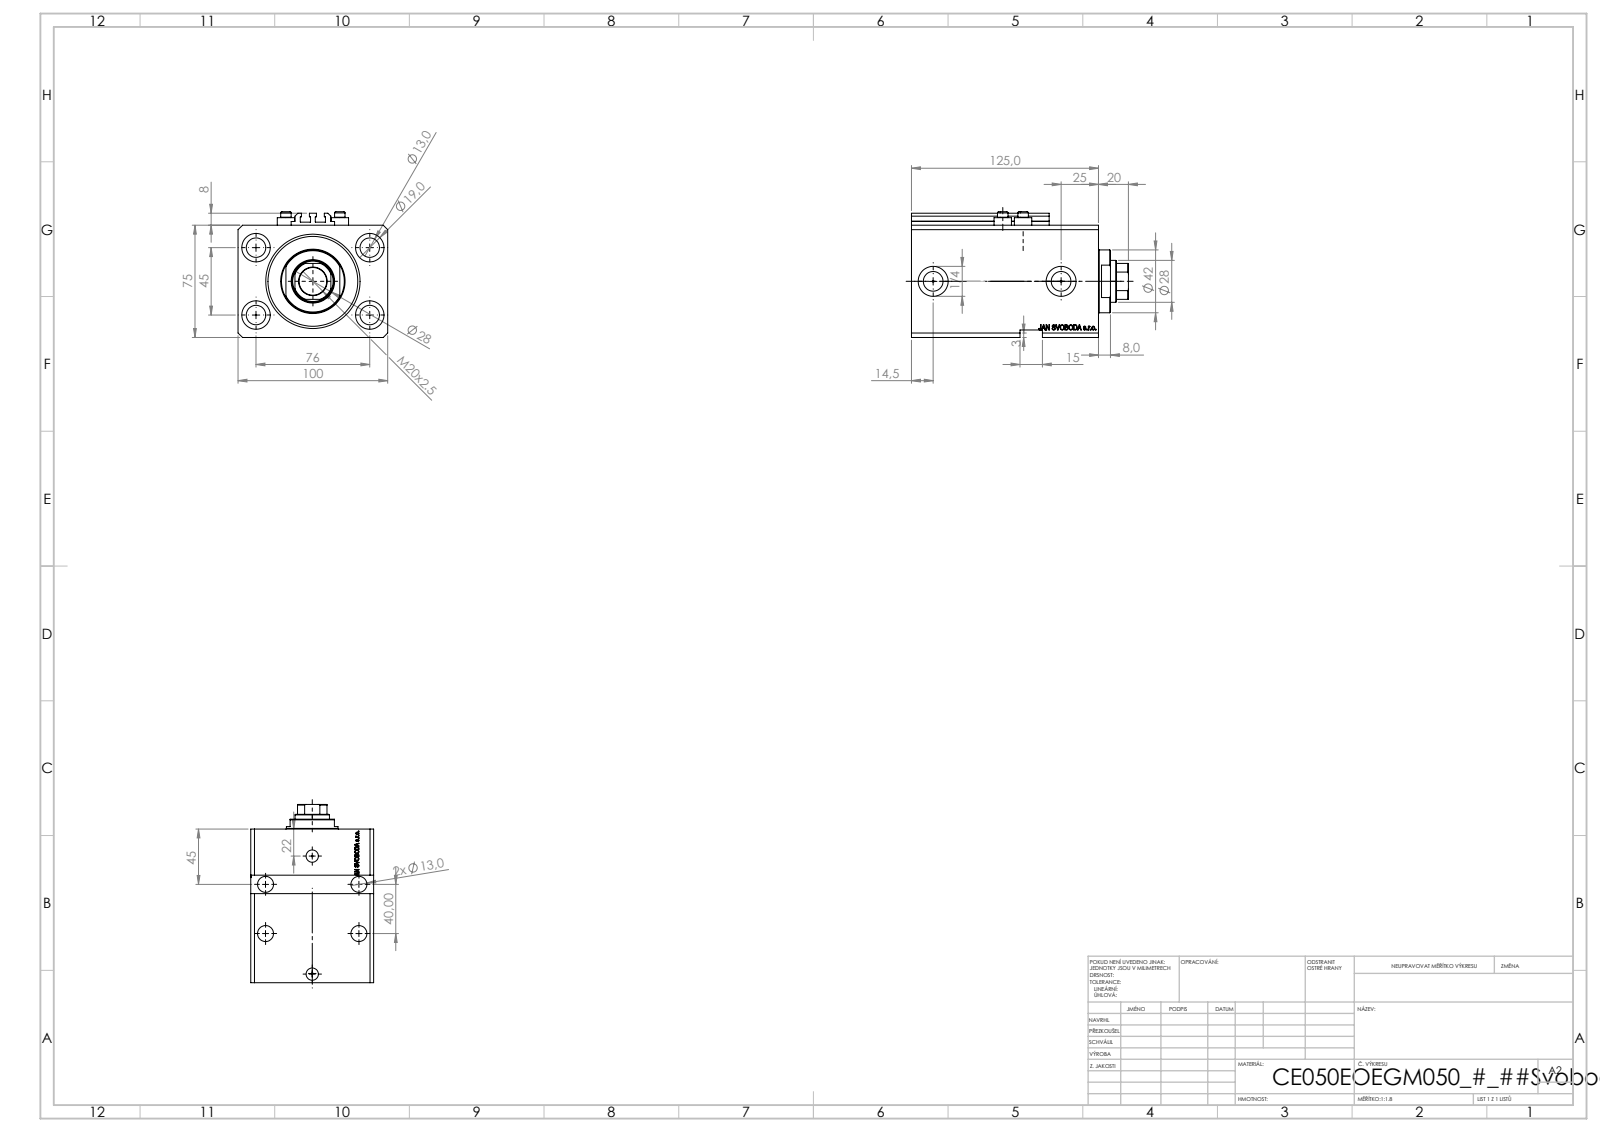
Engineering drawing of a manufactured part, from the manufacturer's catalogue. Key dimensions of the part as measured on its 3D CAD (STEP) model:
Part name (STEP PRODUCT): ALLEN BOLT V250CE; V250CE_E_Body; V250CE_VC_E; V250CE_C_VCP
STEP written by: SolidWorks 2019 (CONFIG_CONTROL_DESIGN)
Units: millimetres
Bodies: 8 solids, 1108 faces (535 planar, 146 cylindrical, 427 other)
Overall size (bounding box): 145 × 100 × 84
Volume: 768 812 mm³ · Surface area: 150 350 mm²
Round holes (diameter × count): ⌀13 ×8, ⌀1.25 ×4, ⌀4 ×4, ⌀19 ×4, ⌀10 ×2, ⌀13.16 ×2, ⌀20 ×2, ⌀18.5 ×1, ⌀28 ×1, ⌀50 ×1, ⌀63 ×1
Round bosses / shafts (diameter × count): ⌀11.6 ×4, ⌀7 ×4, ⌀42 ×1
Partial cylindrical surfaces — rounded edges, fillets, slot ends (radius × count): R0.2 ×10, R13.5 ×1
Main face-to-face distances: 75, 100, 125, 20, 11.9, 113.1, 105, 93.1, 70, 5
Hole centre spacings: 44.16, 76, 13.6, 20.72, 27.59, 29, 33.62, 36
